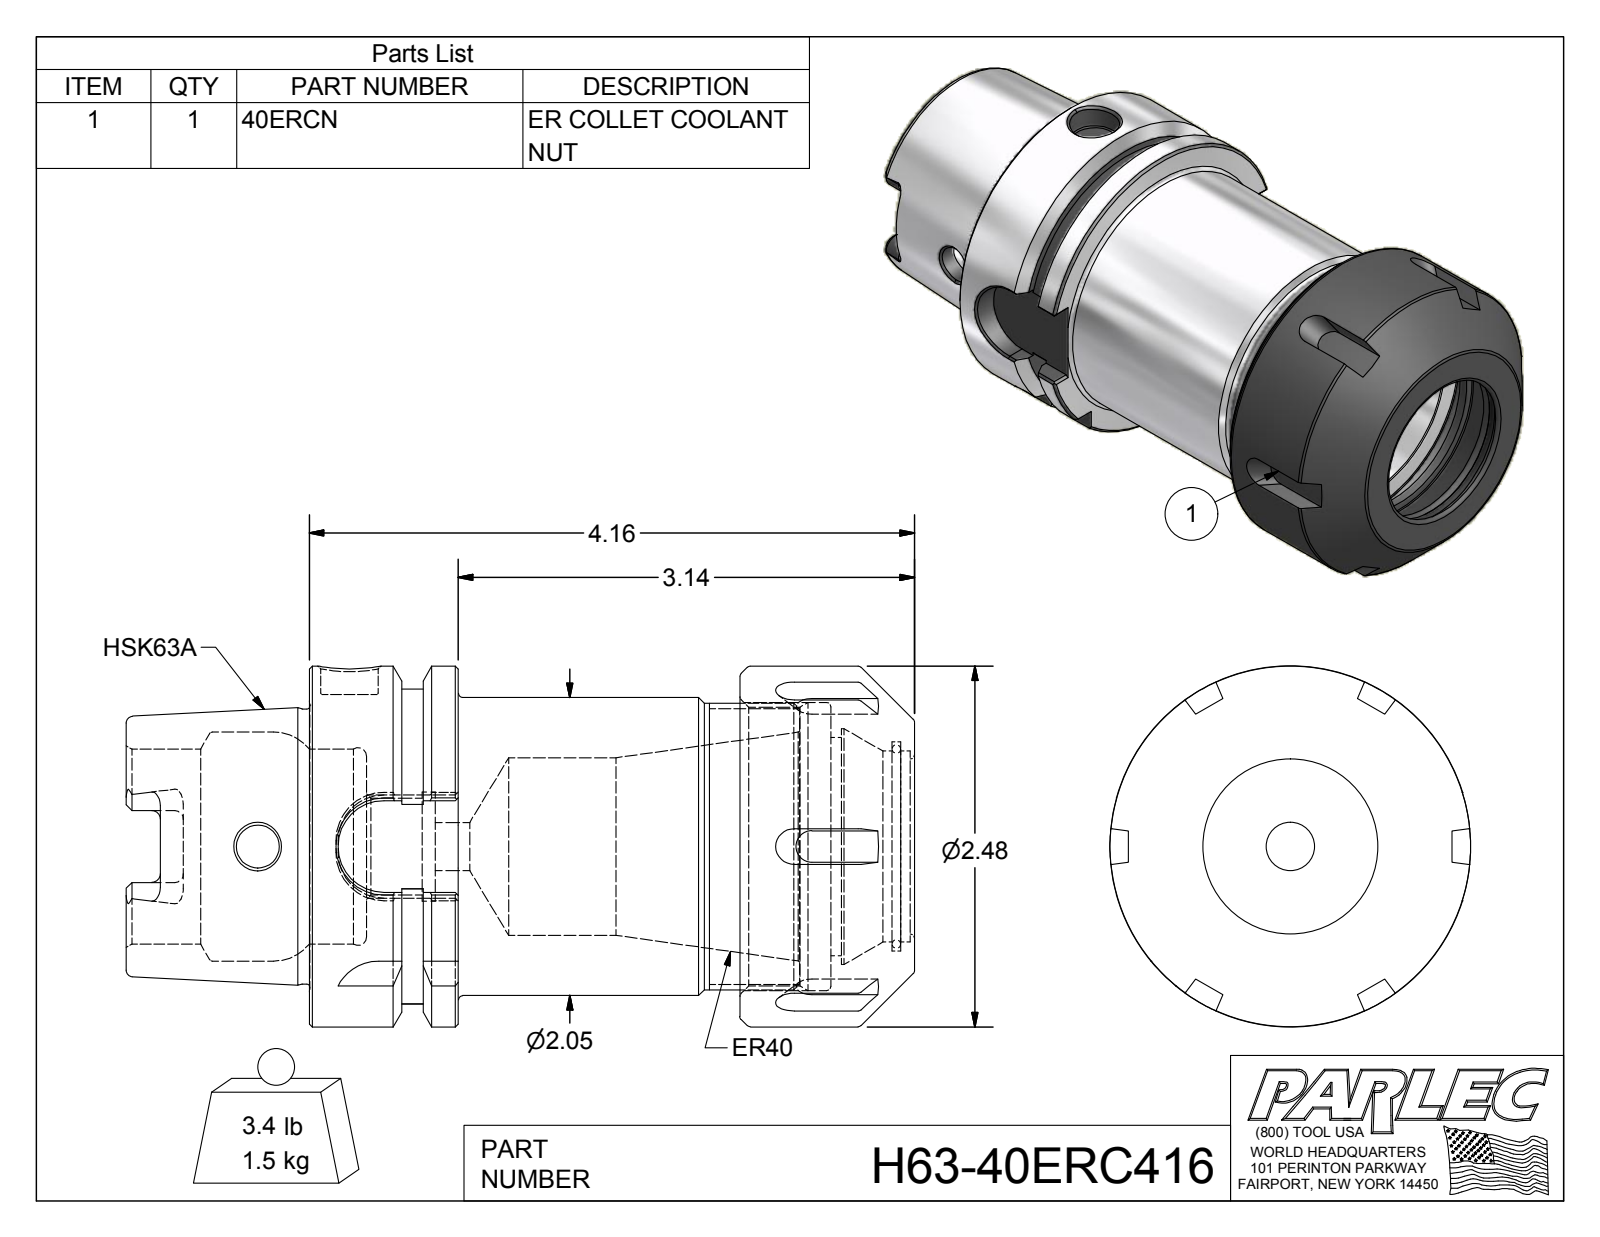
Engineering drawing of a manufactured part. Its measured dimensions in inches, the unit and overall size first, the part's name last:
Units: inches
Overall size (bounding box): 5.42 × 2.48 × 2.48
Round holes (diameter × count): ⌀0.295 ×1, ⌀0.331 ×1, ⌀0.394 ×1, ⌀0.666 ×1, ⌀0.749 ×1, ⌀1.22 ×1, ⌀1.313 ×1, ⌀1.339 ×1, ⌀1.437 ×1, ⌀1.5 ×1, ⌀1.575 ×1, ⌀1.62 ×1
Round bosses / shafts (diameter × count): ⌀2.48 ×1, ⌀2.48 ×1, ⌀2.047 ×1, ⌀1.969 ×1, ⌀1.891 ×1
Partial cylindrical surfaces — rounded edges, fillets, slot ends (radius × count): R0.059 ×6, R0.113 ×4, R0.315 ×4, R1.083 ×1
Main face-to-face distances: 3.585, 1.024, 4.16, 0.575, 0.241, 0.389, 2.561, 3.136, 2.96, 1.936
Volume: 11.98 in³ · Surface area: 80.08 in²
Bodies: 2 solids, 200 faces (82 planar, 44 cylindrical, 74 other)
Part name (STEP PRODUCT): H63-40ERC416; H63-40ER4-1; 40ERCN
STEP written by: Autodesk Inventor 2012 (AUTOMOTIVE_DESIGN)
